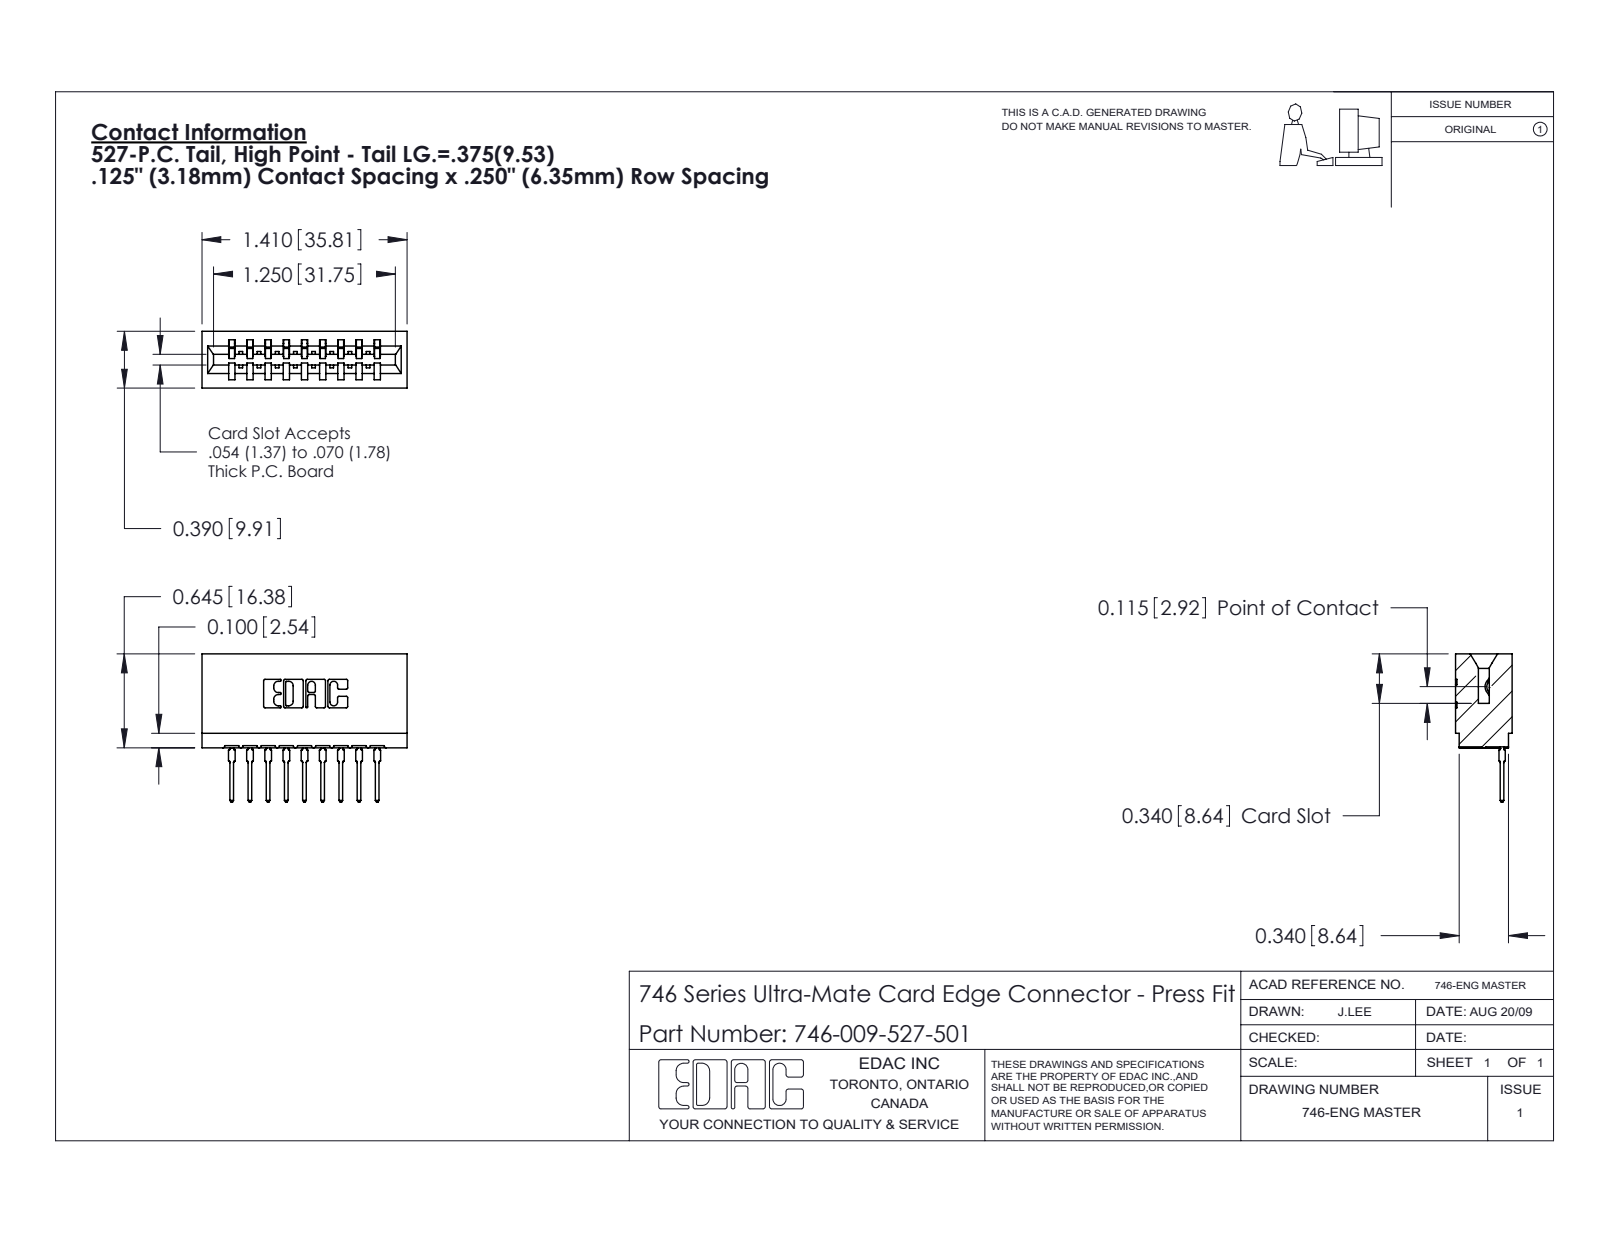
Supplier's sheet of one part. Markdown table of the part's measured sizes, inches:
| quantity | value |
| --- | --- |
| part name | 746-292-001_527; 746 Part_.340 Slot Depth - 01; 746-009-527-501 |
| STEP written by | SolidWorks 2020 (CONFIG_CONTROL_DESIGN) |
| units | inches |
| bodies | 10 solids, 1069 faces (622 planar, 213 cylindrical, 234 other) |
| overall size | 1.41 × 1.019 × 0.39 |
| volume | 0.258 in³ |
| surface area | 8.143 in² |
| partial cylindrical surfaces (radius × count) | 0.01 × 22, 0.021 × 18, 0.015 × 10, 0.007 × 6, 0.031 × 6, 0.005 × 4, 0.011 × 4, 0.026 × 3 |
| main face-to-face distances | 0.25, 0.5, 0.042, 0.333, 0.125, 0.125, 0.292, 0.208, 0.057, 0.375 |
